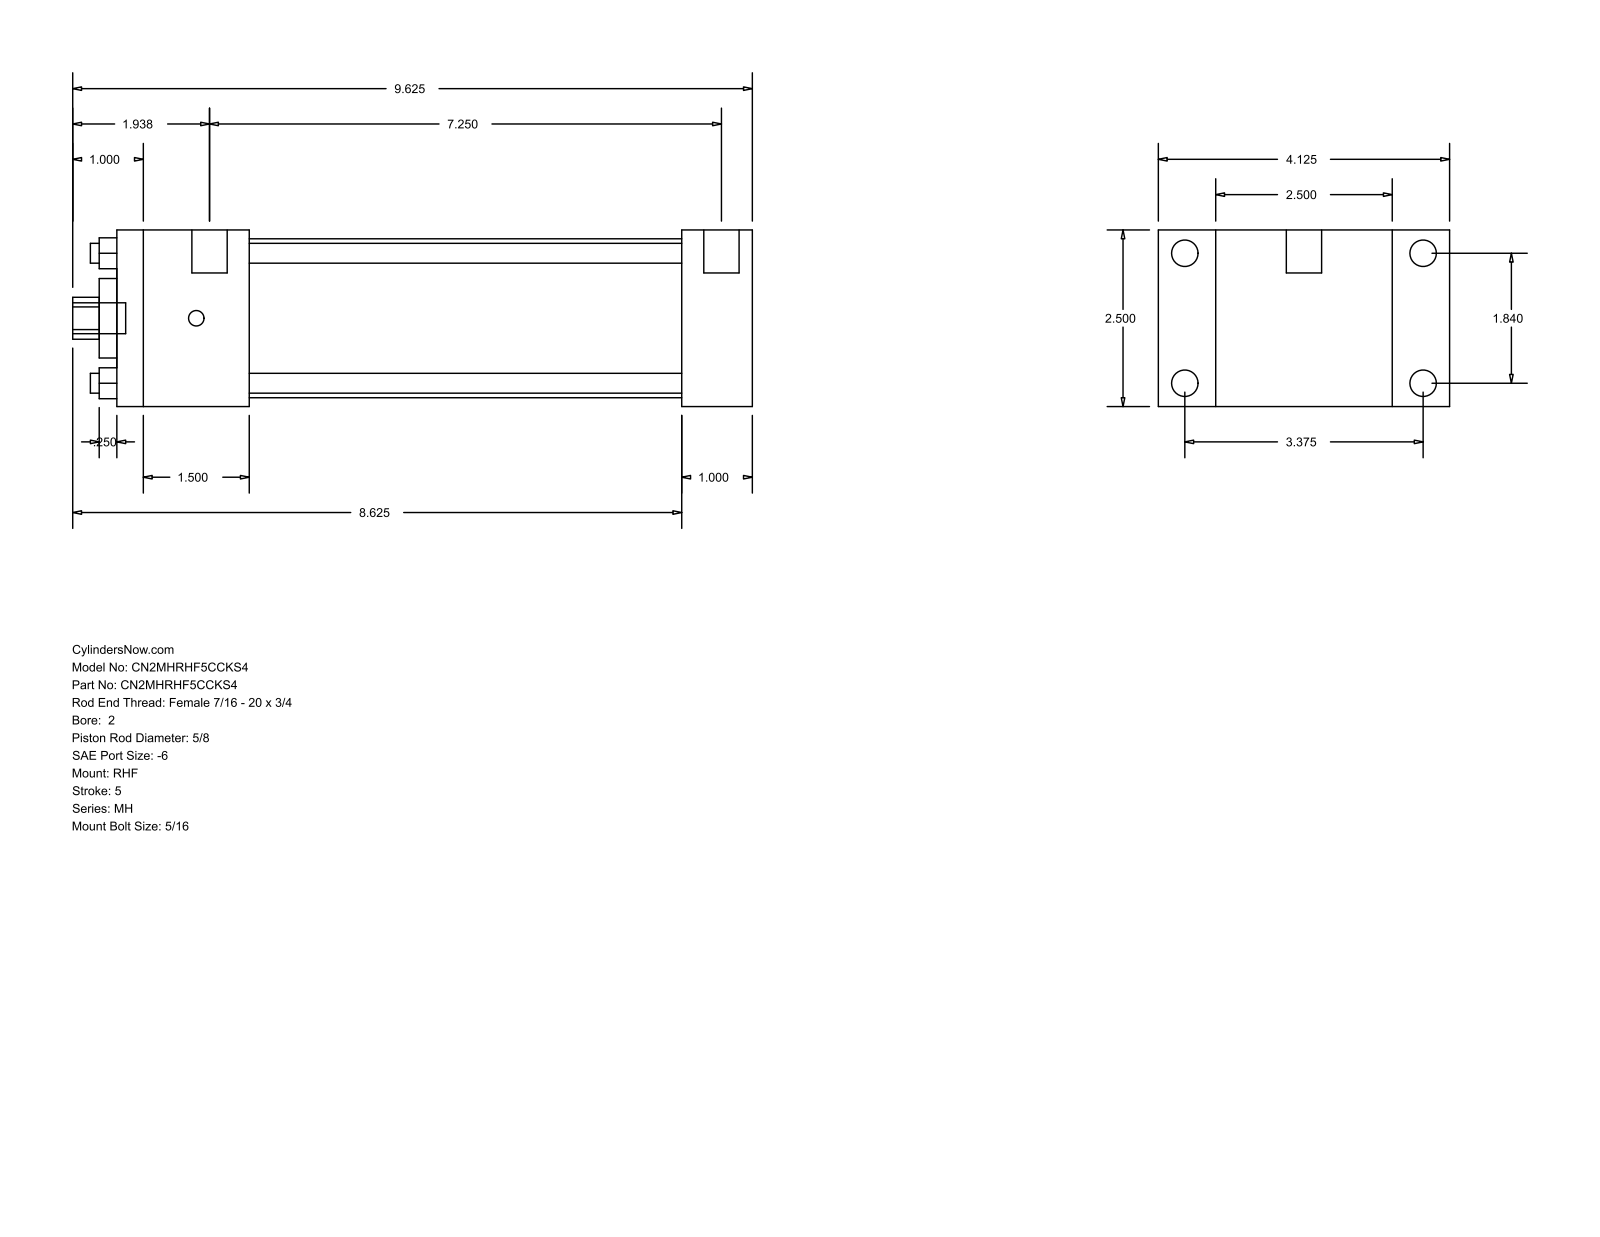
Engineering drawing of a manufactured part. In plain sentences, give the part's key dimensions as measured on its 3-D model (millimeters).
The part is named "MH_RHF__0200_0.625". Its 3-D file was written by "GSSL Pune (CONFIG_CONTROL_DESIGN)". It is 0 solids with 88 faces: 60 planar, 28 cylindrical and 0 other. Overall it measures 244.47 by 104.78 by 63.5 millimeters. Round holes: 4 of diameter 7.14, 1 of diameter 15.88, 1 of diameter 28.57, 1 of diameter 57.15. Round bosses or shafts: 4 of diameter 9.53, 4 of diameter 5.56, 2 of diameter 12.7, 1 of diameter 11.11. Partial cylindrical surfaces (rounded edges, fillets, slot ends): 1 of radius 7.54. The main face-to-face distances are 63.5, 25.4, 20.64, 84.14, 203.19, 228.59, 104.78, 47.62, 155.57, 180.97. The hole center spacings are 33.05, 46.74, 66.1.
